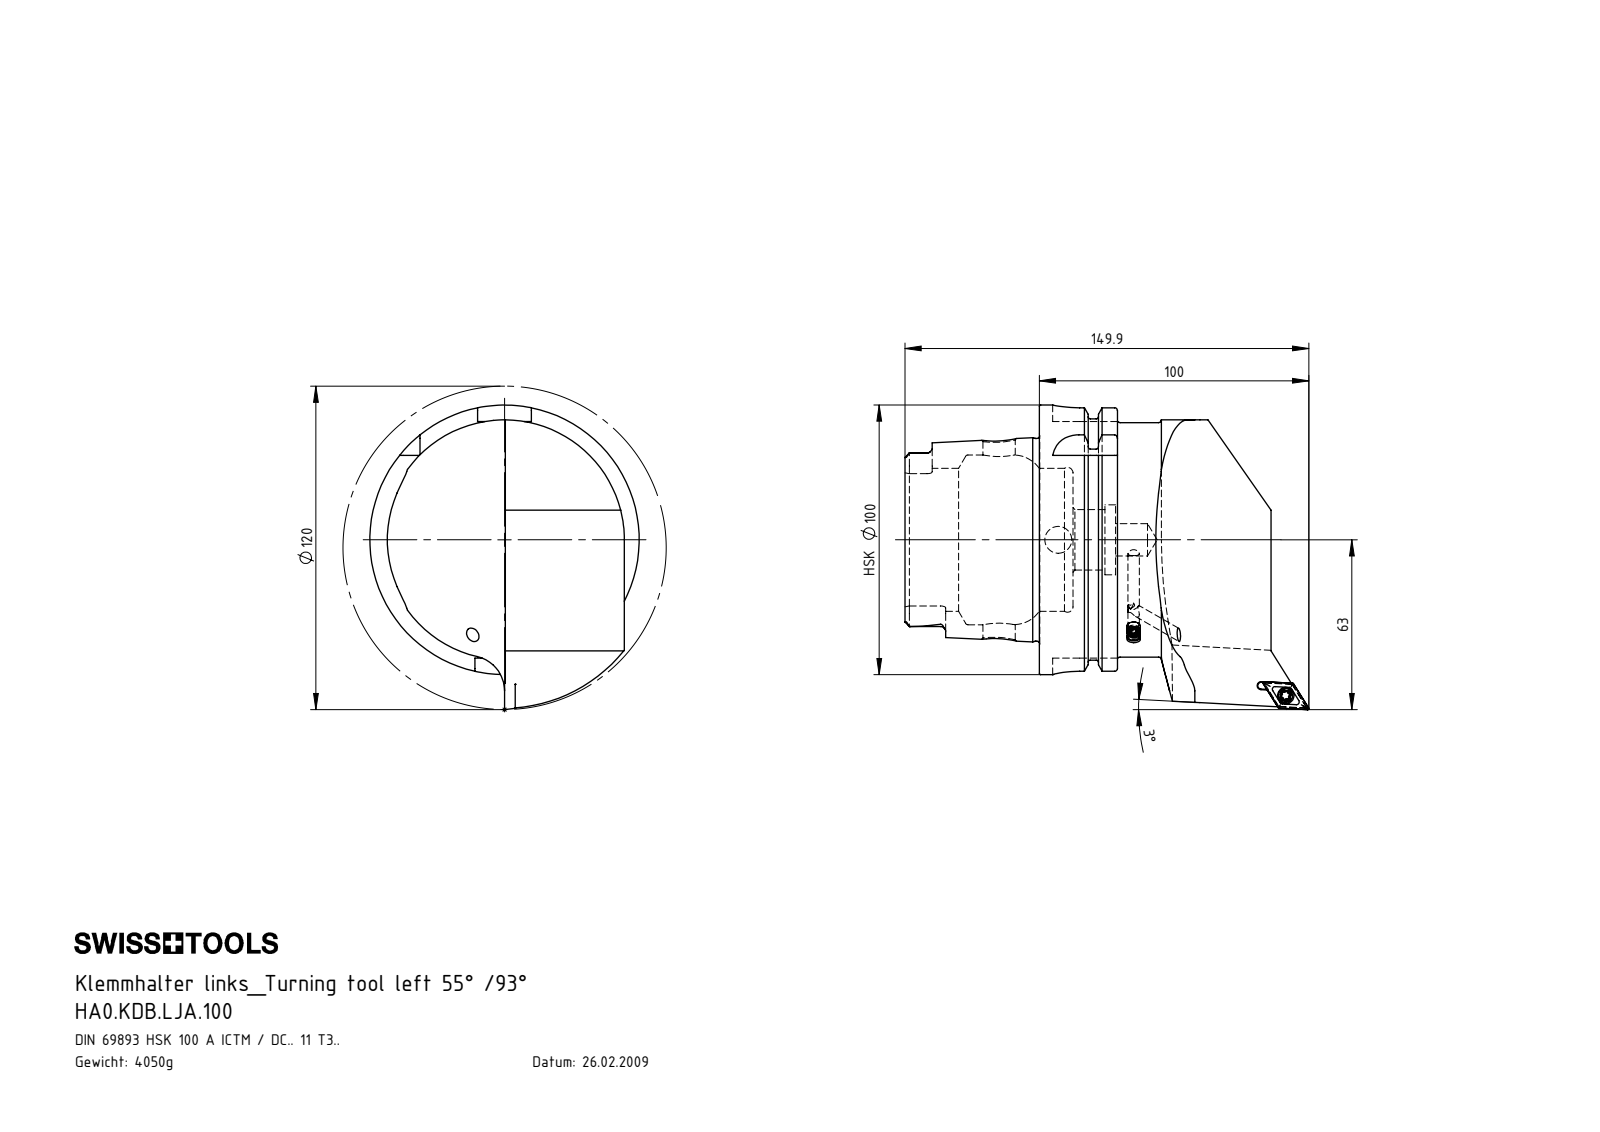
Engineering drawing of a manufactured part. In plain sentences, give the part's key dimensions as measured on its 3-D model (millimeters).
The part is named "HA0-KDB.LJA.100; KVT_MB_600_050; WCB-ER2.001.009_A; DCMT11T304 (+1 more)". Its 3-D file was written by "SolidWorks 2012 (AUTOMOTIVE_DESIGN)". It is 5 solids with 310 faces: 75 planar, 94 cylindrical and 141 other. Overall it measures 149.91 by 113 by 100 millimeters. Its volume is 515 679 cubic millimeters and its surface area 67 759 square millimeters. Round holes: 2 of diameter 4.2, 2 of diameter 12, 1 of diameter 3.3, 1 of diameter 4, 1 of diameter 4.4, 1 of diameter 6.1, 1 of diameter 10, 1 of diameter 22.5, 1 of diameter 26, 1 of diameter 53, 1 of diameter 63. Round bosses or shafts: 1 of diameter 100, 1 of diameter 91.95, 1 of diameter 87, 1 of diameter 75.26, 1 of diameter 5.25, 1 of diameter 5, 1 of diameter 4. Partial cylindrical surfaces (rounded edges, fillets, slot ends): 6 of radius 0.34, 6 of radius 0.59, 6 of radius 1.9, 4 of radius 10, 2 of radius 4.83, 2 of radius 4.88, 1 of radius 1.25, 1 of radius 6. The main face-to-face distances are 86, 44.2, 12.45, 73.55, 28.95, 16.5, 57.05, 49.9, 62.35, 78.85. The hole center spacings are 102.22, 102.34.
